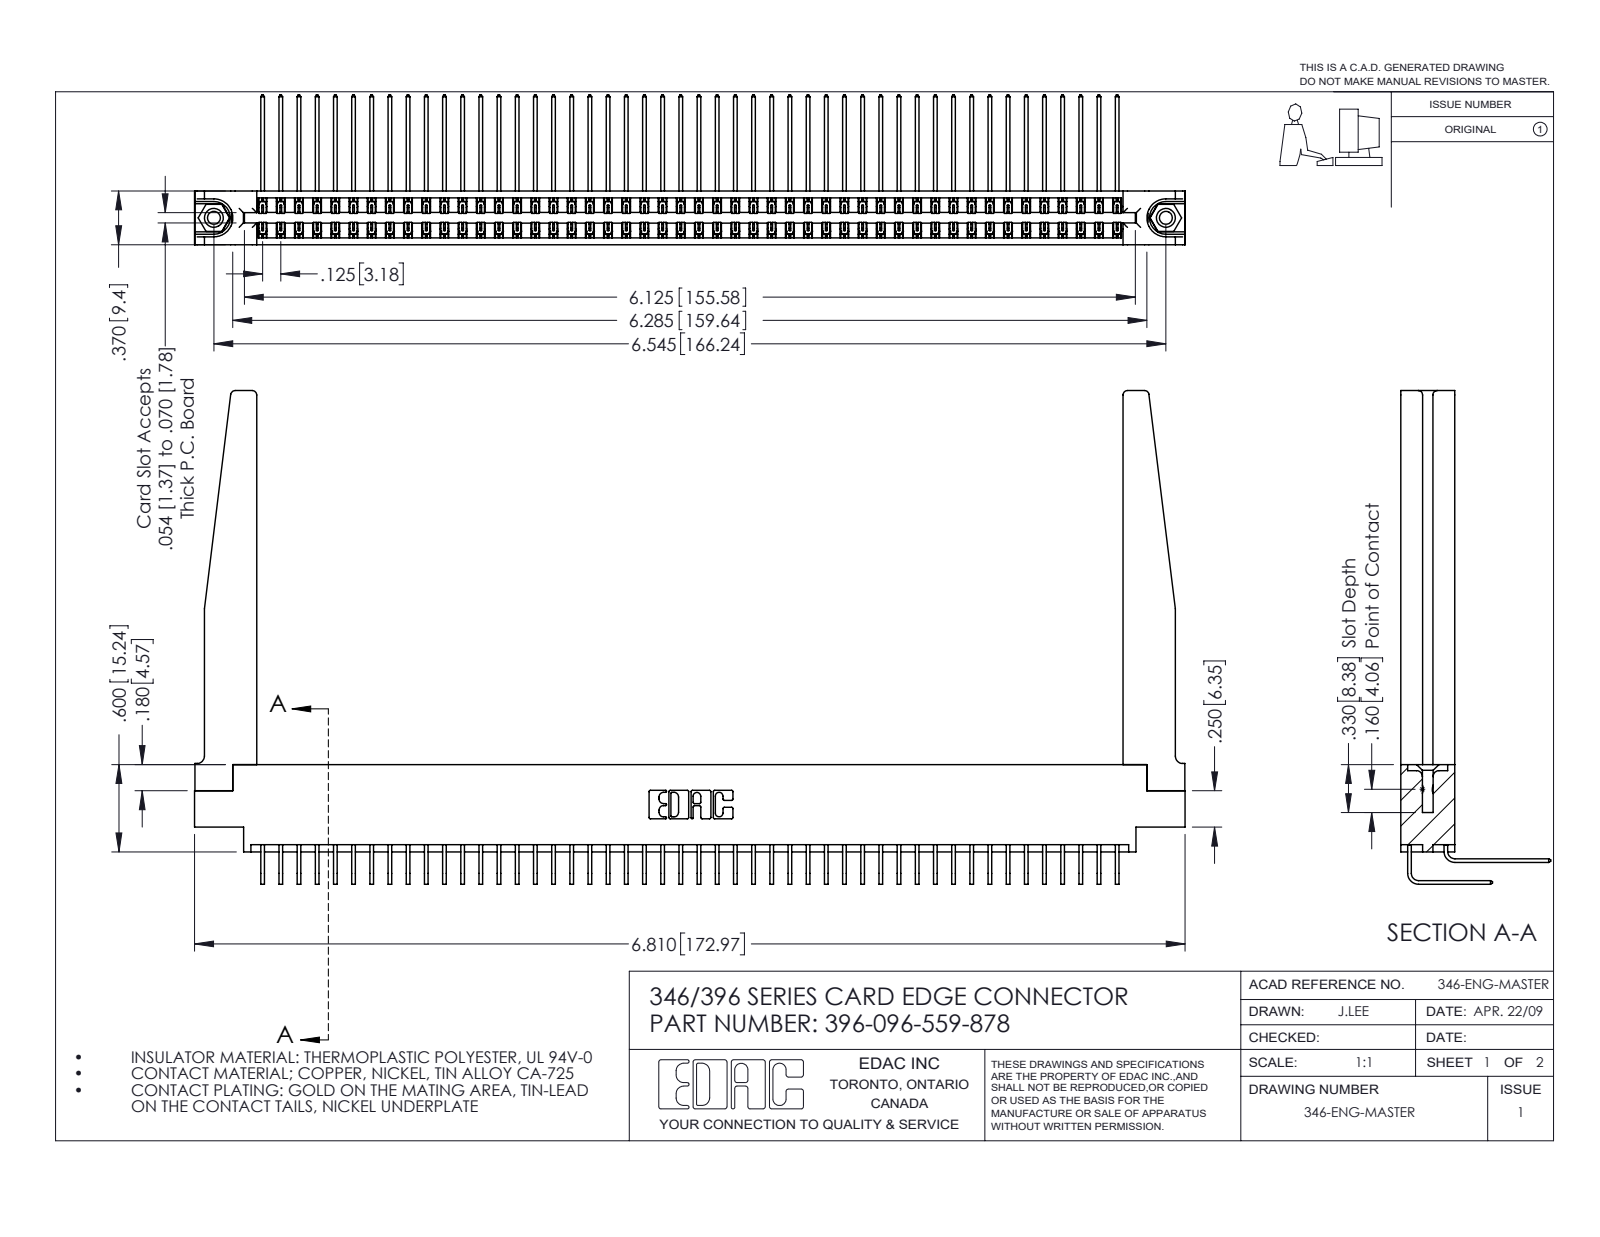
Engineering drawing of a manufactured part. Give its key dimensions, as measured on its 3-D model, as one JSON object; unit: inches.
{"part_name": "396-096-559-878; 345-292-001_558 559 Tail - 1; 345-292-001_559 Tail - 2; 345-250-001_345-250-001-102 (+2 more)", "step_written_by": "SolidWorks 2016 (CONFIG_CONTROL_DESIGN)", "units": "inches", "bodies": {"solids": 101, "faces": 5544, "planar": 3774, "cylindrical": 1718, "other": 52}, "overall_size": [6.81, 3.393, 1.03], "volume_in3": 1.478, "surface_area_in2": 51.56, "round_holes": [[0.089, 2], [0.125, 2], [0.156, 2], [0.064, 1]], "round_bosses_or_shafts": [[0.155, 2]], "partial_cylinders_radius": [[0.006, 144], [0.01, 22], [0.03, 8], [0.007, 6], [0.031, 6], [0.05, 4], [0.026, 3], [0.014, 2]], "face_to_face_distances": [0.37, 0.048, 0.322, 0.072, 0.025, 0.25, 0.148, 0.15, 0.298, 0.275], "hole_center_spacings": [0.246, 6.336, 6.545]}
